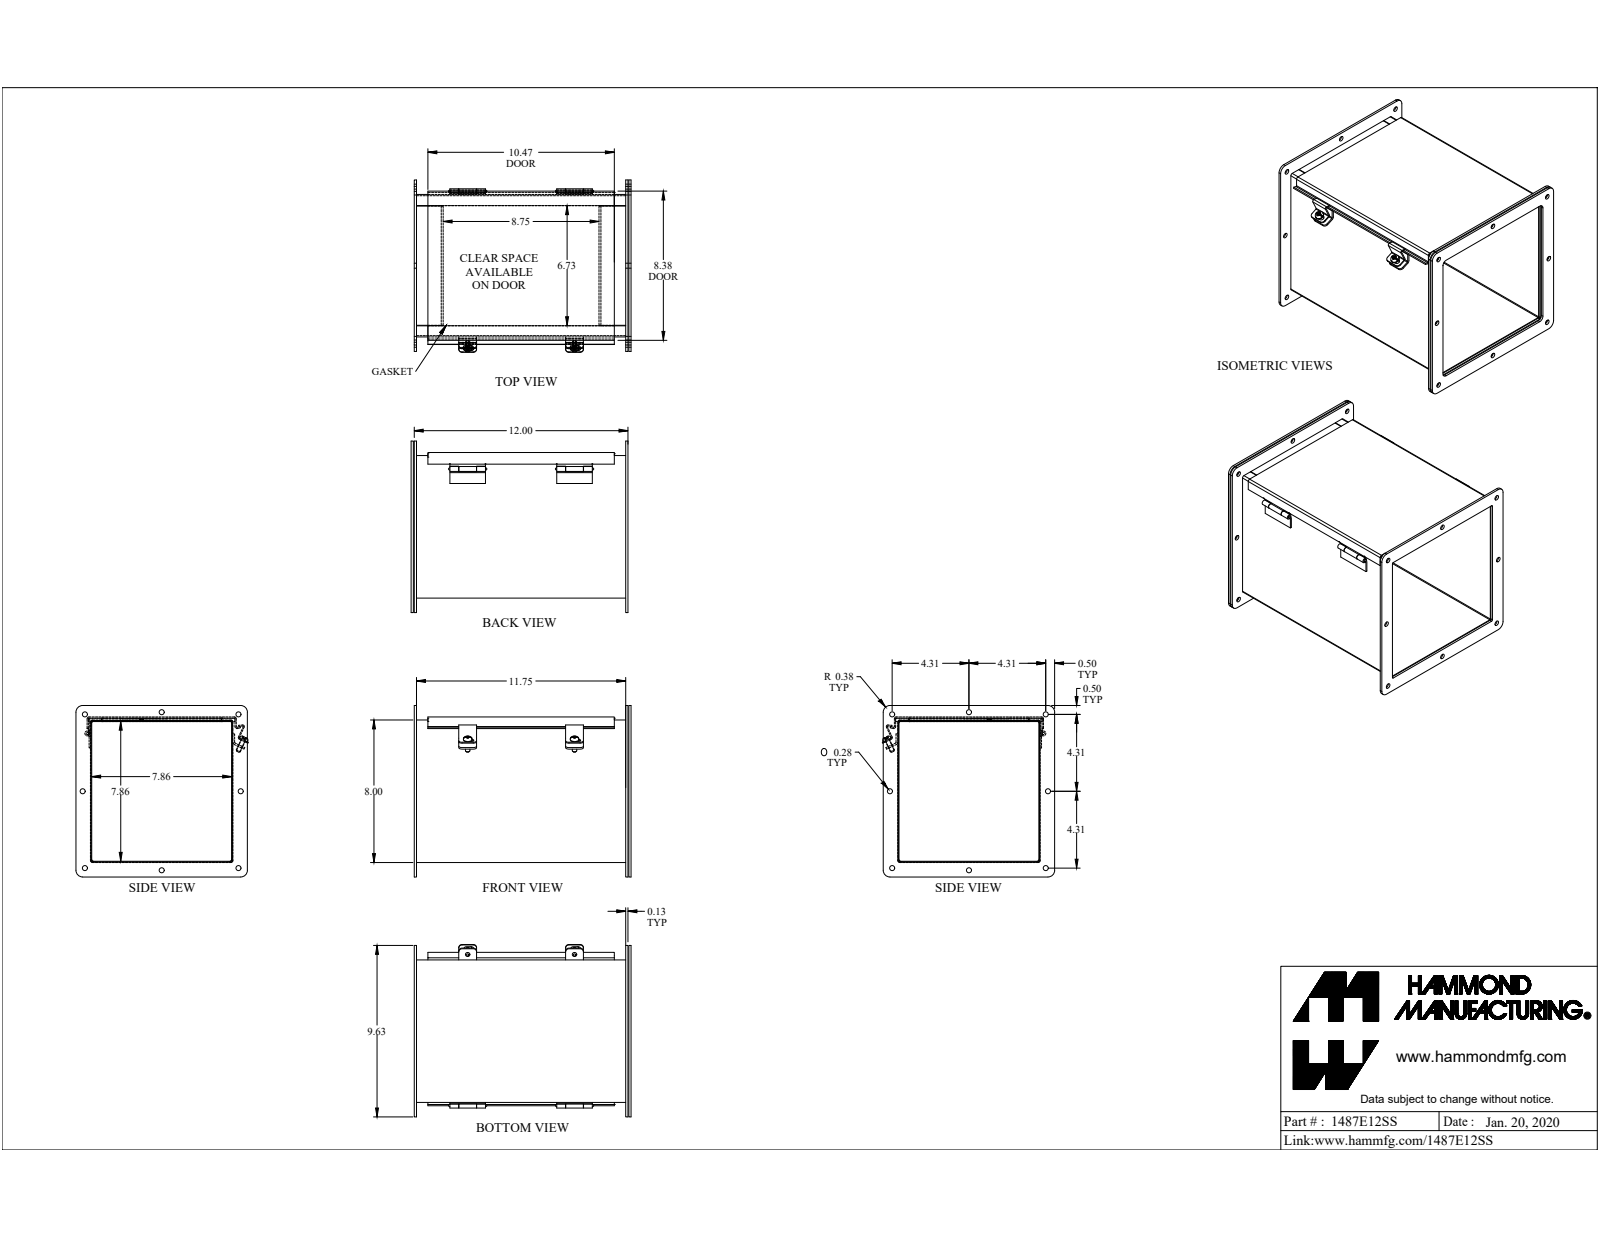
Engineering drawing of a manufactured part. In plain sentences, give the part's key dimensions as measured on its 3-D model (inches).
The part is named "1487E12SS". Its 3-D file was written by "SolidWorks 2019 (CONFIG_CONTROL_DESIGN)". It is 27 solids with 554 faces: 350 planar, 152 cylindrical and 52 other. Overall it measures 12.546 by 9.677 by 9.625 inches. Its volume is 47.11 cubic inches and its surface area 1 164 square inches. Round holes: 8 of diameter 0.281, 2 of diameter 0.213, 1 of diameter 0.187, 1 of diameter 0.196, 1 of diameter 0.258, 1 of diameter 0.35. Round bosses or shafts: 3 of diameter 0.25, 2 of diameter 0.48, 1 of diameter 0.5, 1 of diameter 0.337, 1 of diameter 0.18. Partial cylindrical surfaces (rounded edges, fillets, slot ends): 8 of radius 0.188, 8 of radius 0.375, 7 of radius 0.036, 7 of radius 0.108, 6 of radius 0.02, 4 of radius 0.03, 4 of radius 0.063, 4 of radius 0.141. The main face-to-face distances are 0.072, 7.928, 8.1, 8, 7.856, 8.028, 0.125, 8.172, 0.172, 0.175. The hole center spacings are 4.315, 9.755, 6.276, 4.314, 8.625, 8.625, 9.755, 12.198.
